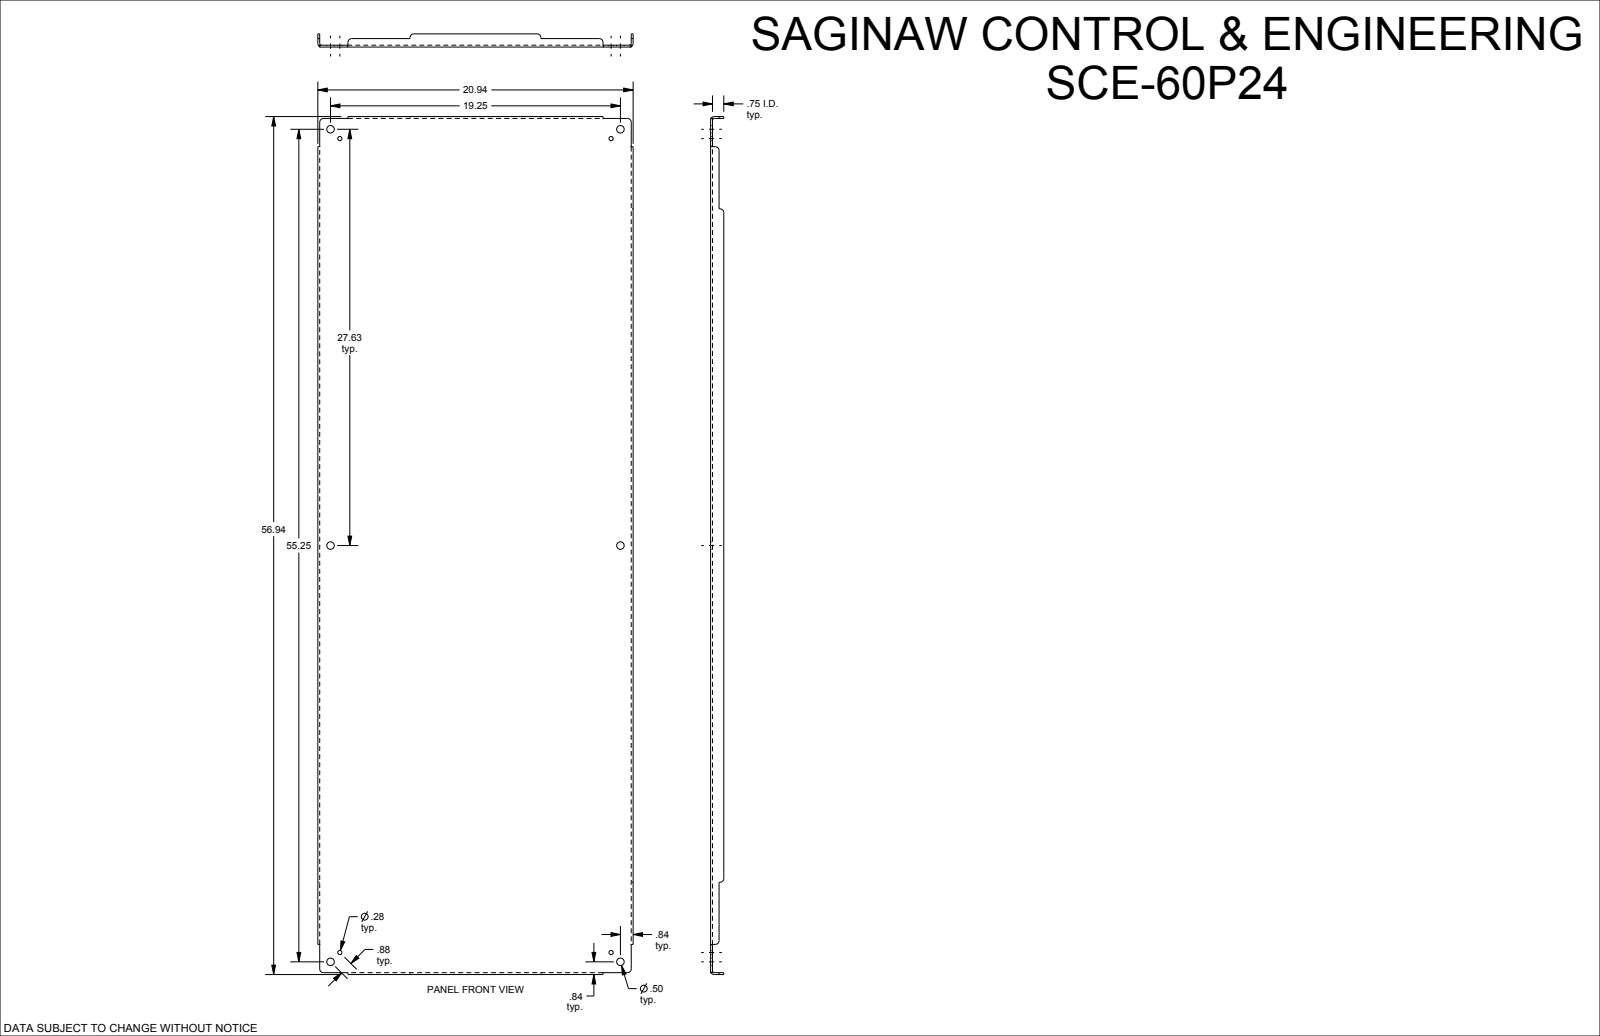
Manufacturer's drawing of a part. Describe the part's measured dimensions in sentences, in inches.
The part is named "SCE-60P24". Its 3-D file was written by "SolidWorks 2019 (CONFIG_CONTROL_DESIGN)". It is 1 solid with 108 faces: 46 planar, 38 cylindrical and 24 other. Overall it measures 56.938 by 20.938 by 0.875 inches. Its volume is 159.1 cubic inches and its surface area 2 567 square inches. Round holes: 6 of diameter 0.5, 4 of diameter 0.281. Partial cylindrical surfaces (rounded edges, fillets, slot ends): 12 of radius 0.25, 4 of radius 0.112, 4 of radius 0.237. The main face-to-face distances are 0.125, 0.125, 20.813, 20.687, 20.938, 56.813, 0.75, 0.875, 56.687, 56.938. The hole center spacings are 0.875, 18.641, 27.013, 27.625, 32.809, 33.67, 54.635, 57.72.
